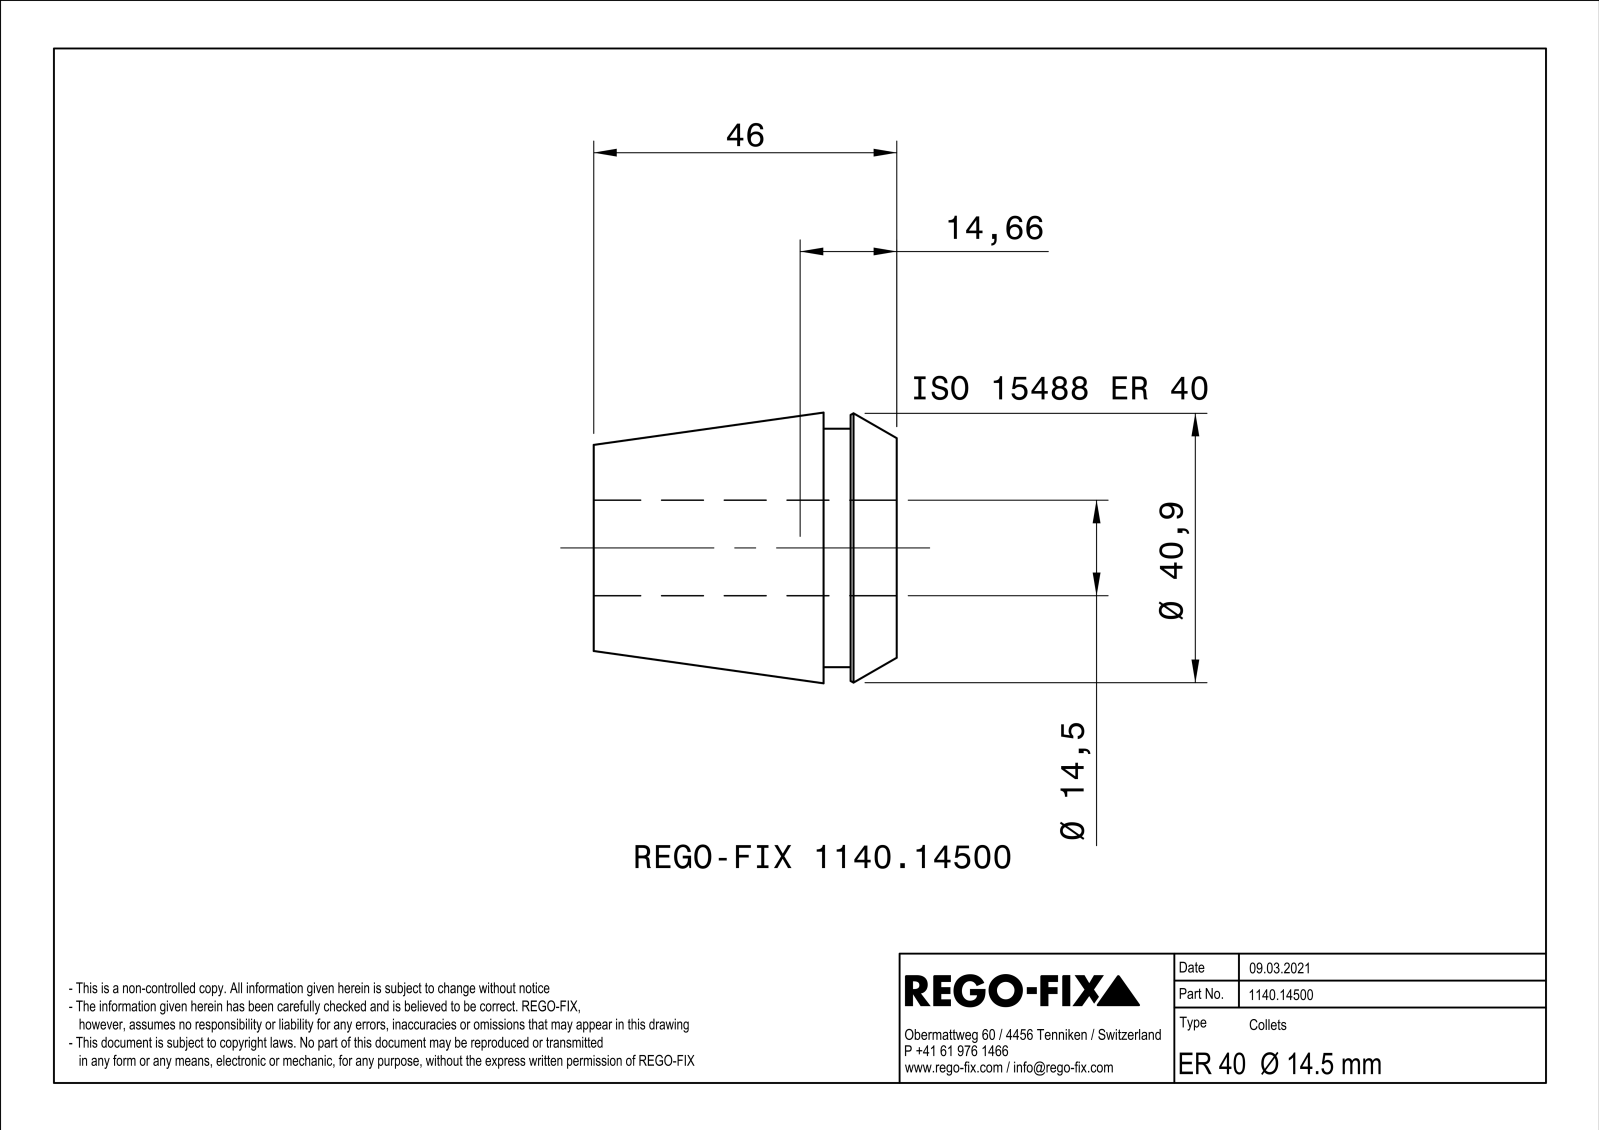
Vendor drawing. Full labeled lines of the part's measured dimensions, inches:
Part name (STEP PRODUCT): NOCUT
STEP written by: SIEMENS PLM Software Solid Edge ST10 (AUTOMOTIVE_DESIGN)
Units: inches
Bodies: 1 solid, 177 faces (88 planar, 9 cylindrical, 80 other)
Overall size (bounding box): 1.811 × 1.614 × 1.614
Volume: 2.022 in³ · Surface area: 34.35 in²
Round holes (diameter × count): ⌀0.571 ×1
Round bosses / shafts (diameter × count): ⌀1.425 ×1
Main face-to-face distances: 0.039, 1.811, 0.437, 1.374, 0.276, 0.161, 1.535, 0.295, 0.02, 0.142
